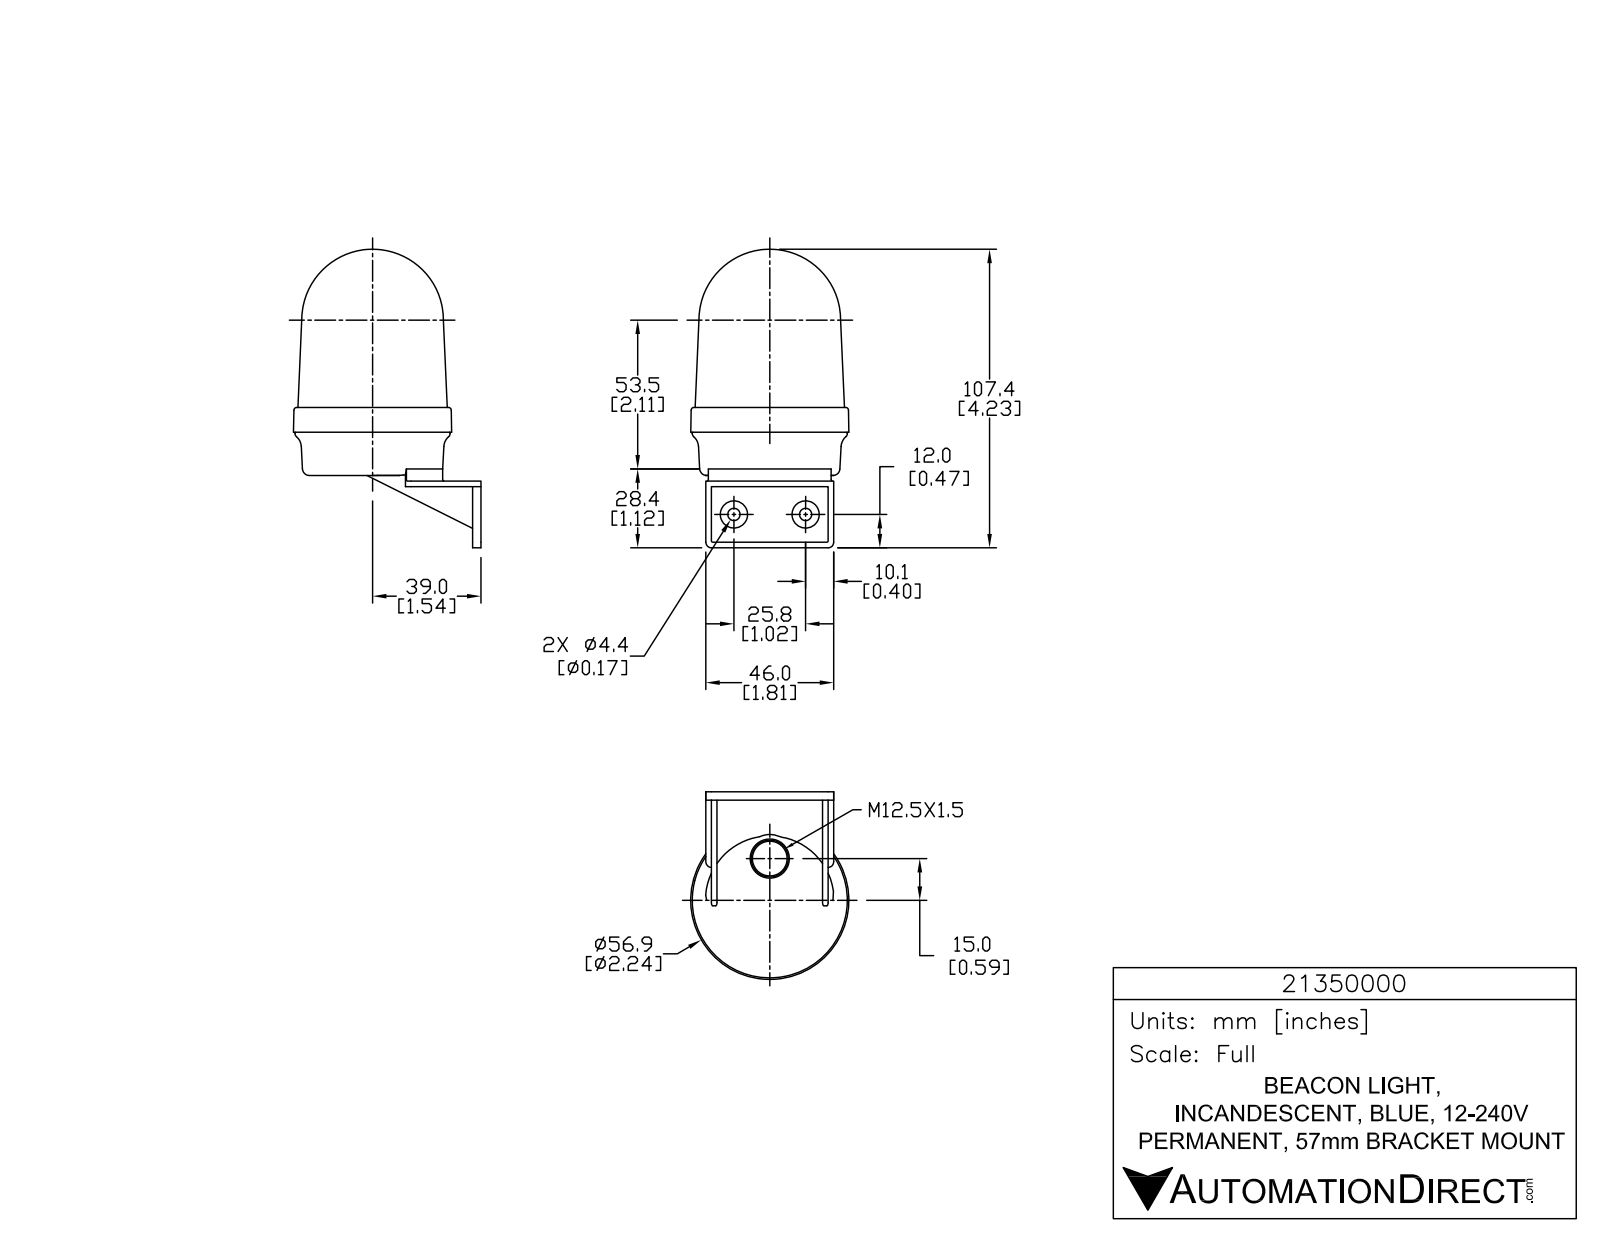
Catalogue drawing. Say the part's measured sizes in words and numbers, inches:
The part is named "21350000". Its 3-D file was written by "SolidWorks 2015 (AUTOMOTIVE_DESIGN)". It is 1 solid with 826 faces: 550 planar, 178 cylindrical and 98 other. Overall it measures 4.228 by 2.838 by 2.392 inches. Its volume is 9.936 cubic inches and its surface area 32.97 square inches. Round holes: 3 of diameter 0.039, 2 of diameter 0.173. Round bosses or shafts: 3 of diameter 0.226, 3 of diameter 0.056, 2 of diameter 0.386, 1 of diameter 2.197. Partial cylindrical surfaces (rounded edges, fillets, slot ends): 6 of radius 0.008, 6 of radius 0.008, 6 of radius 0.008, 6 of radius 0.02, 6 of radius 0.131, 4 of radius 0.079, 3 of radius 0.004, 3 of radius 0.005. The main face-to-face distances are 0.079, 0.157, 1.575, 1.654, 0.039, 0.118, 1.496, 0.866, 0.945, 0.772. The hole center spacings are 1.016.
